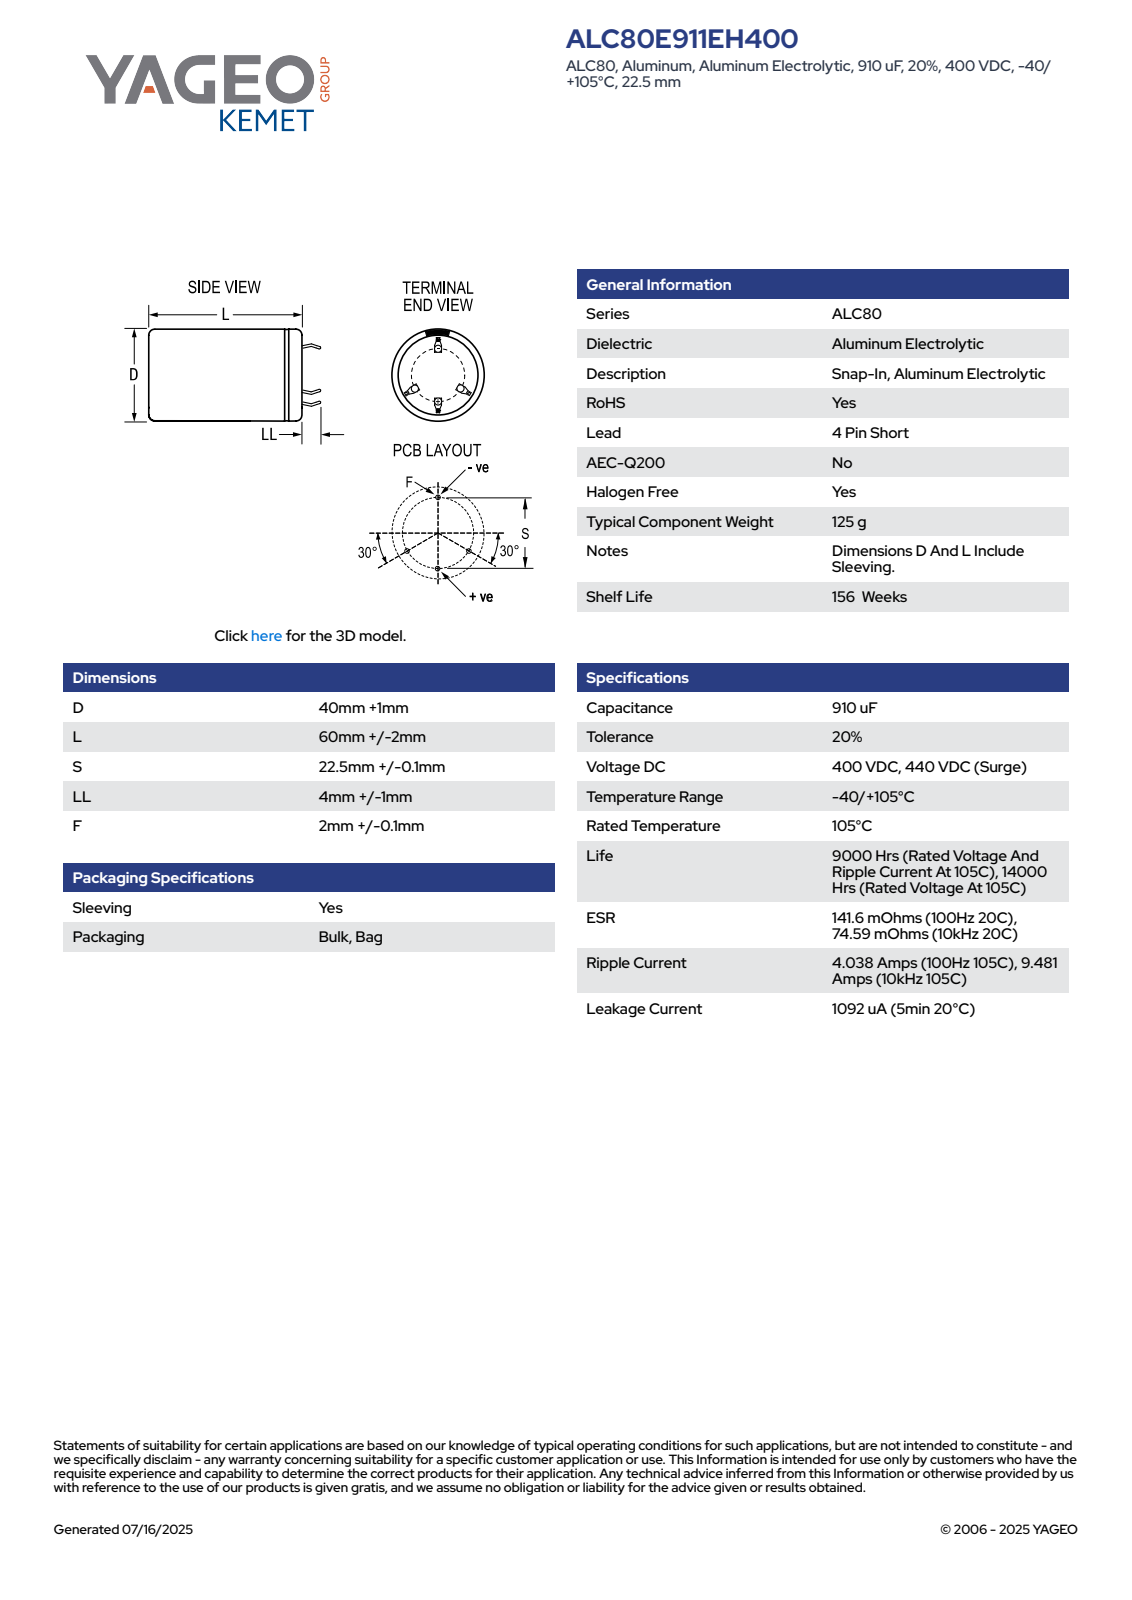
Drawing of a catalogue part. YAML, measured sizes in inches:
part_name: "CARS_K4P_40X60_D41L62S22.5LL5F2.1"
step_written_by: "SolidWorks 2014 (AUTOMOTIVE_DESIGN)"
units: inches
bodies: {solids: 1, faces: 134, planar: 80, cylindrical: 15, other: 39}
overall_size: [2.637, 1.614, 1.614]
volume: 4.948
surface_area: 16.52
round_holes:
  - {diameter: 1.428, count: 1}
round_bosses_or_shafts:
  - {diameter: 1.614, count: 1}
partial_cylinders:
  - {radius: 0.807, count: 1}
face_to_face_distances: [2.441, 2.46, 0.02, 0.024, 0.574, 0.03, 0.053, 0.586, 0.563, 0.083]
